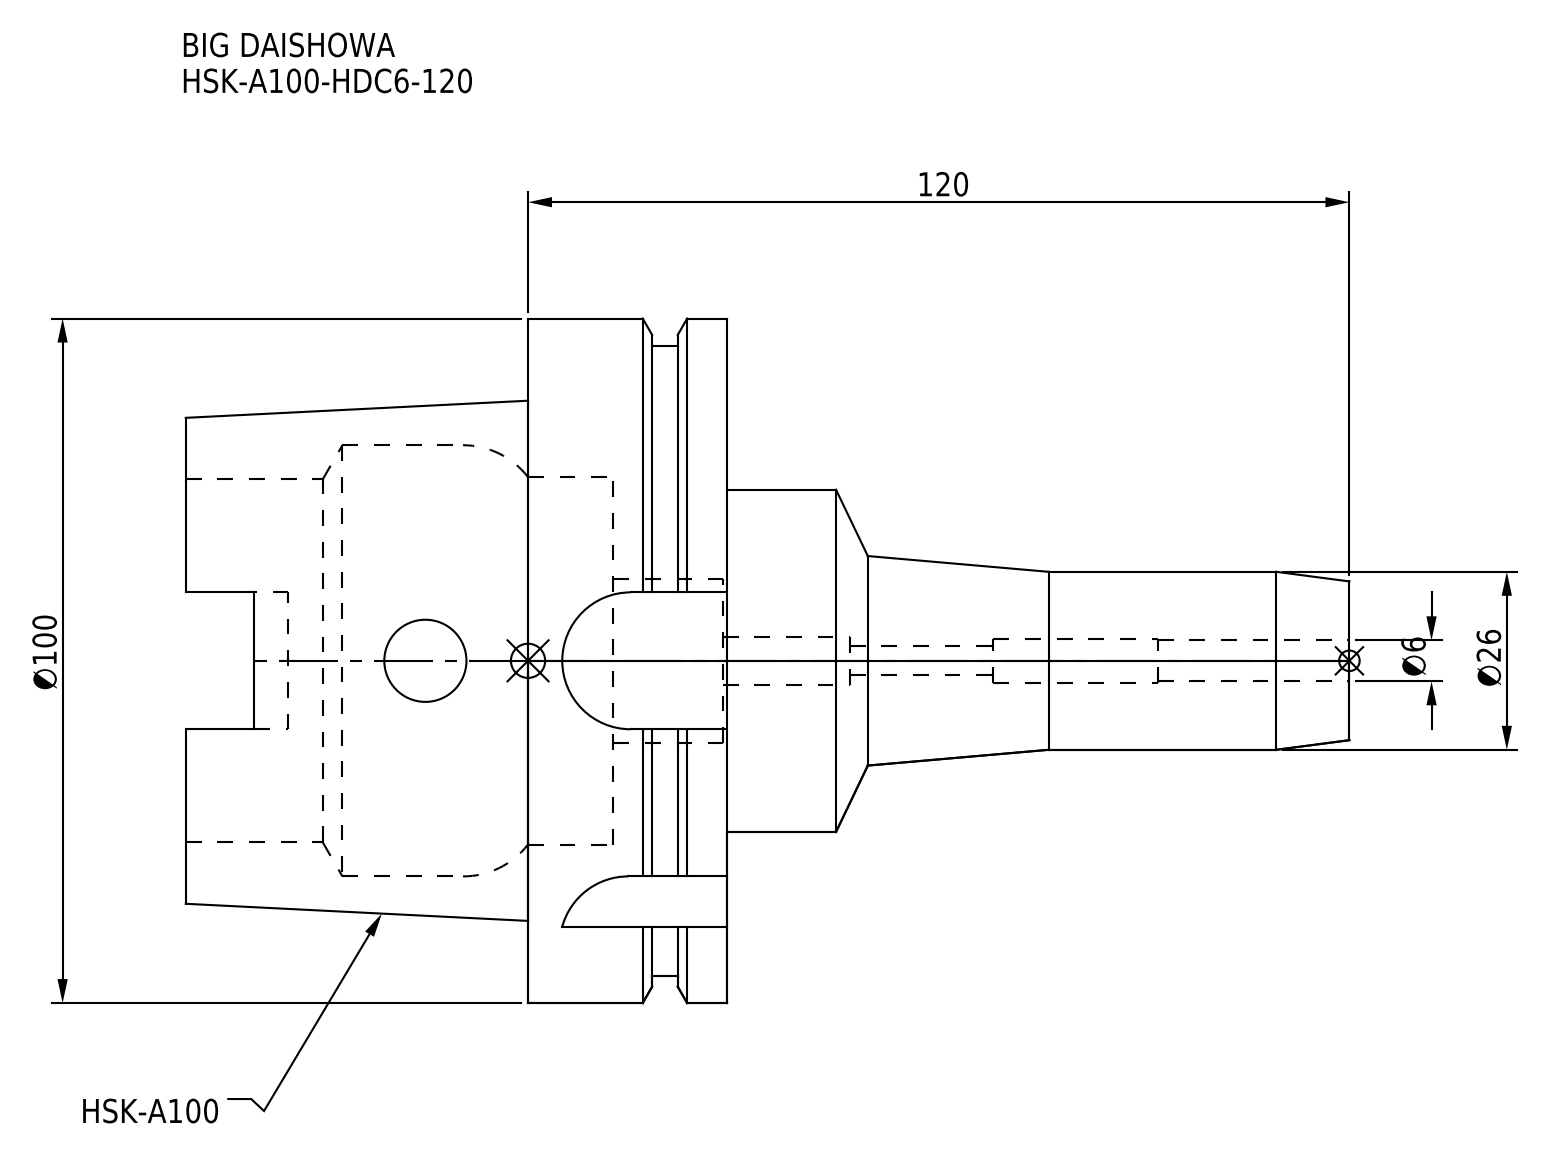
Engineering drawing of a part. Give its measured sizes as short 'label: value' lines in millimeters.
name: HSK-A100-HDC6-120
written by: CREO PARAMETRIC BY PTC INC, 2016380 (AUTOMOTIVE_DESIGN)
unit: mm
bodies: 1 solid, 97 faces (35 planar, 42 cylindrical, 20 other)
size: 170 × 100 × 100
volume: 327 758 mm³; area: 59 920 mm²
holes: 1× ⌀4.2, 1× ⌀6, 1× ⌀6.5, 1× ⌀7, 1× ⌀12, 1× ⌀24, 1× ⌀53, 1× ⌀53.8, 1× ⌀63
bosses: 1× ⌀100, 1× ⌀92, 1× ⌀50, 1× ⌀26
rounds: 4× R4.88, 4× R10
face distances: 29, 16.55, 12.45, 79, 62.45, 50, 88, 0.55, 16, 28.45
